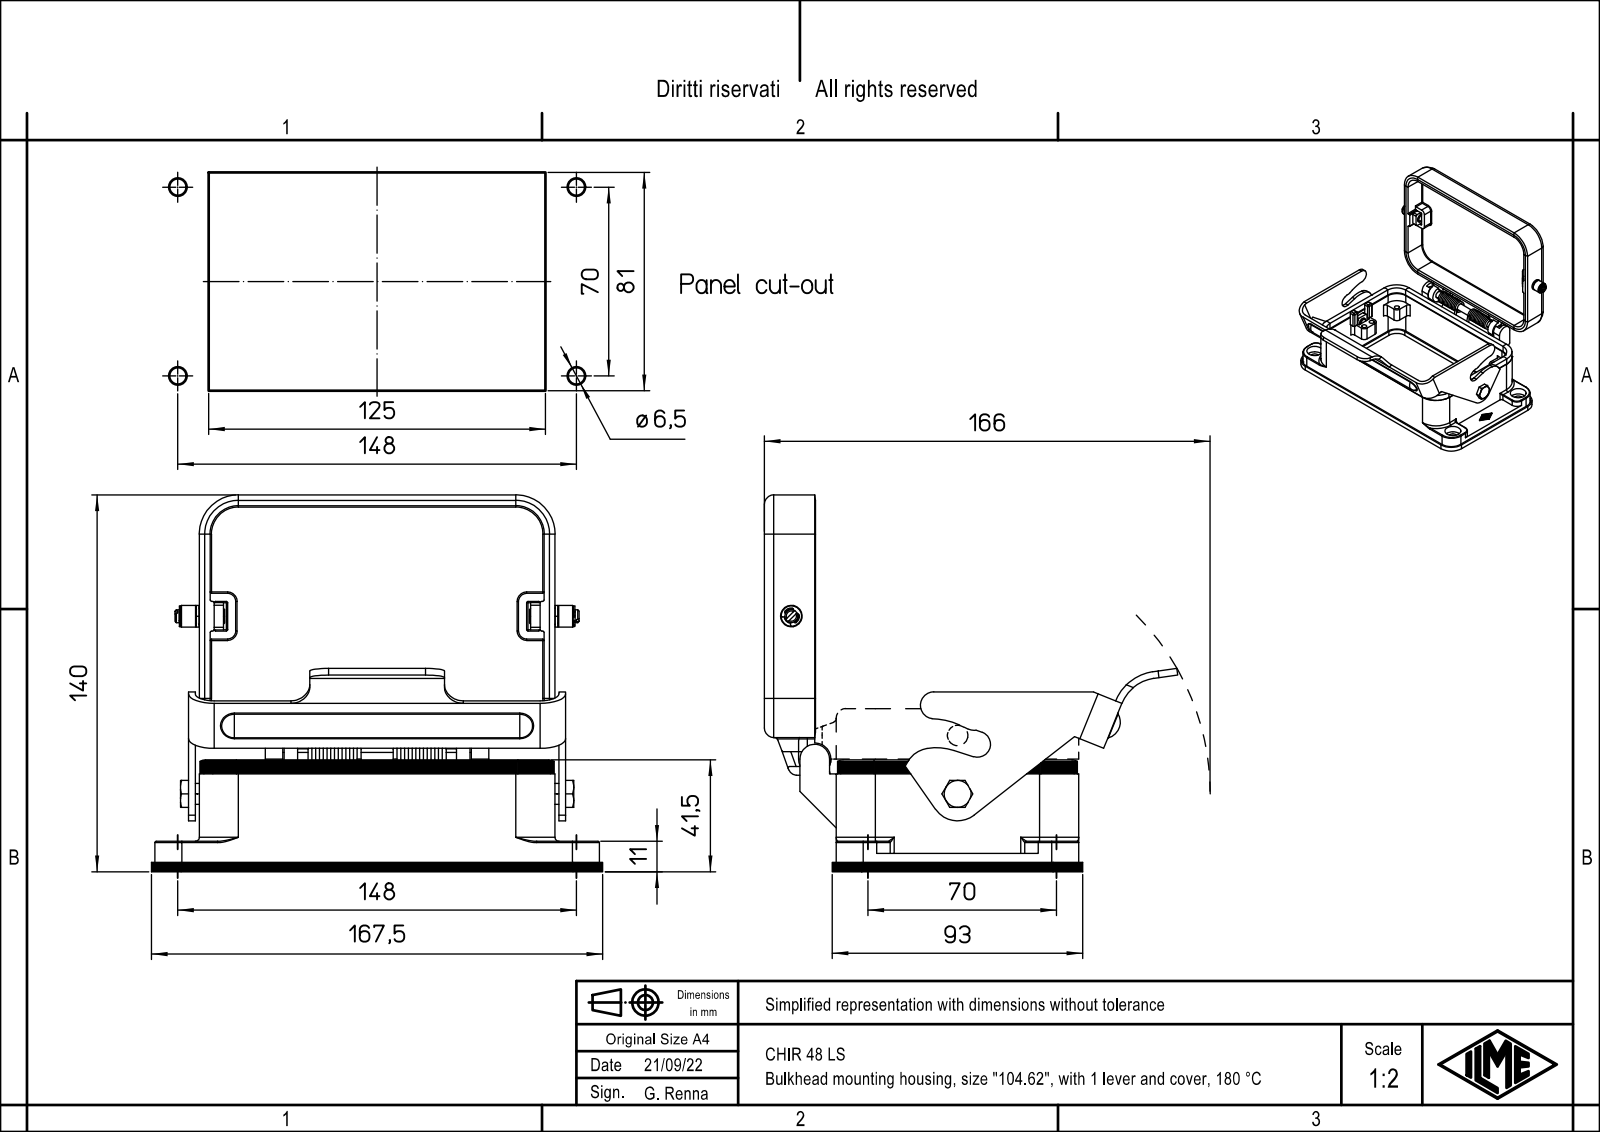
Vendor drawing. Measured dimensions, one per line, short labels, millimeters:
name: CHIR 48 LS
written by: Autodesk Inventor 7 (AUTOMOTIVE_DESIGN)
unit: mm
bodies: 6 solids, 798 faces (218 planar, 303 cylindrical, 277 other)
size: 167.5 × 166.2 × 140.2
volume: 230 406 mm³; area: 113 912 mm²
holes: 4× ⌀2.46, 4× ⌀3.1, 4× ⌀6.5, 4× ⌀6.6, 4× ⌀12, 1× ⌀5.95, 1× ⌀6, 1× ⌀8
bosses: 2× ⌀1.2, 1× ⌀8, 1× ⌀7.8, 1× ⌀6.2, 1× ⌀6, 1× ⌀5, 1× ⌀4.5, 1× ⌀3.5
rounds: 35× R1, 14× R0.38, 13× R0.5, 12× R11, 10× R3, 8× R16, 5× R4, 5× R10
face distances: 5, 86, 114, 28, 14, 9, 130.5, 81, 91, 100
hole spacings: 22.36, 27, 38.01, 44.78, 69.57, 70, 104, 107.45
